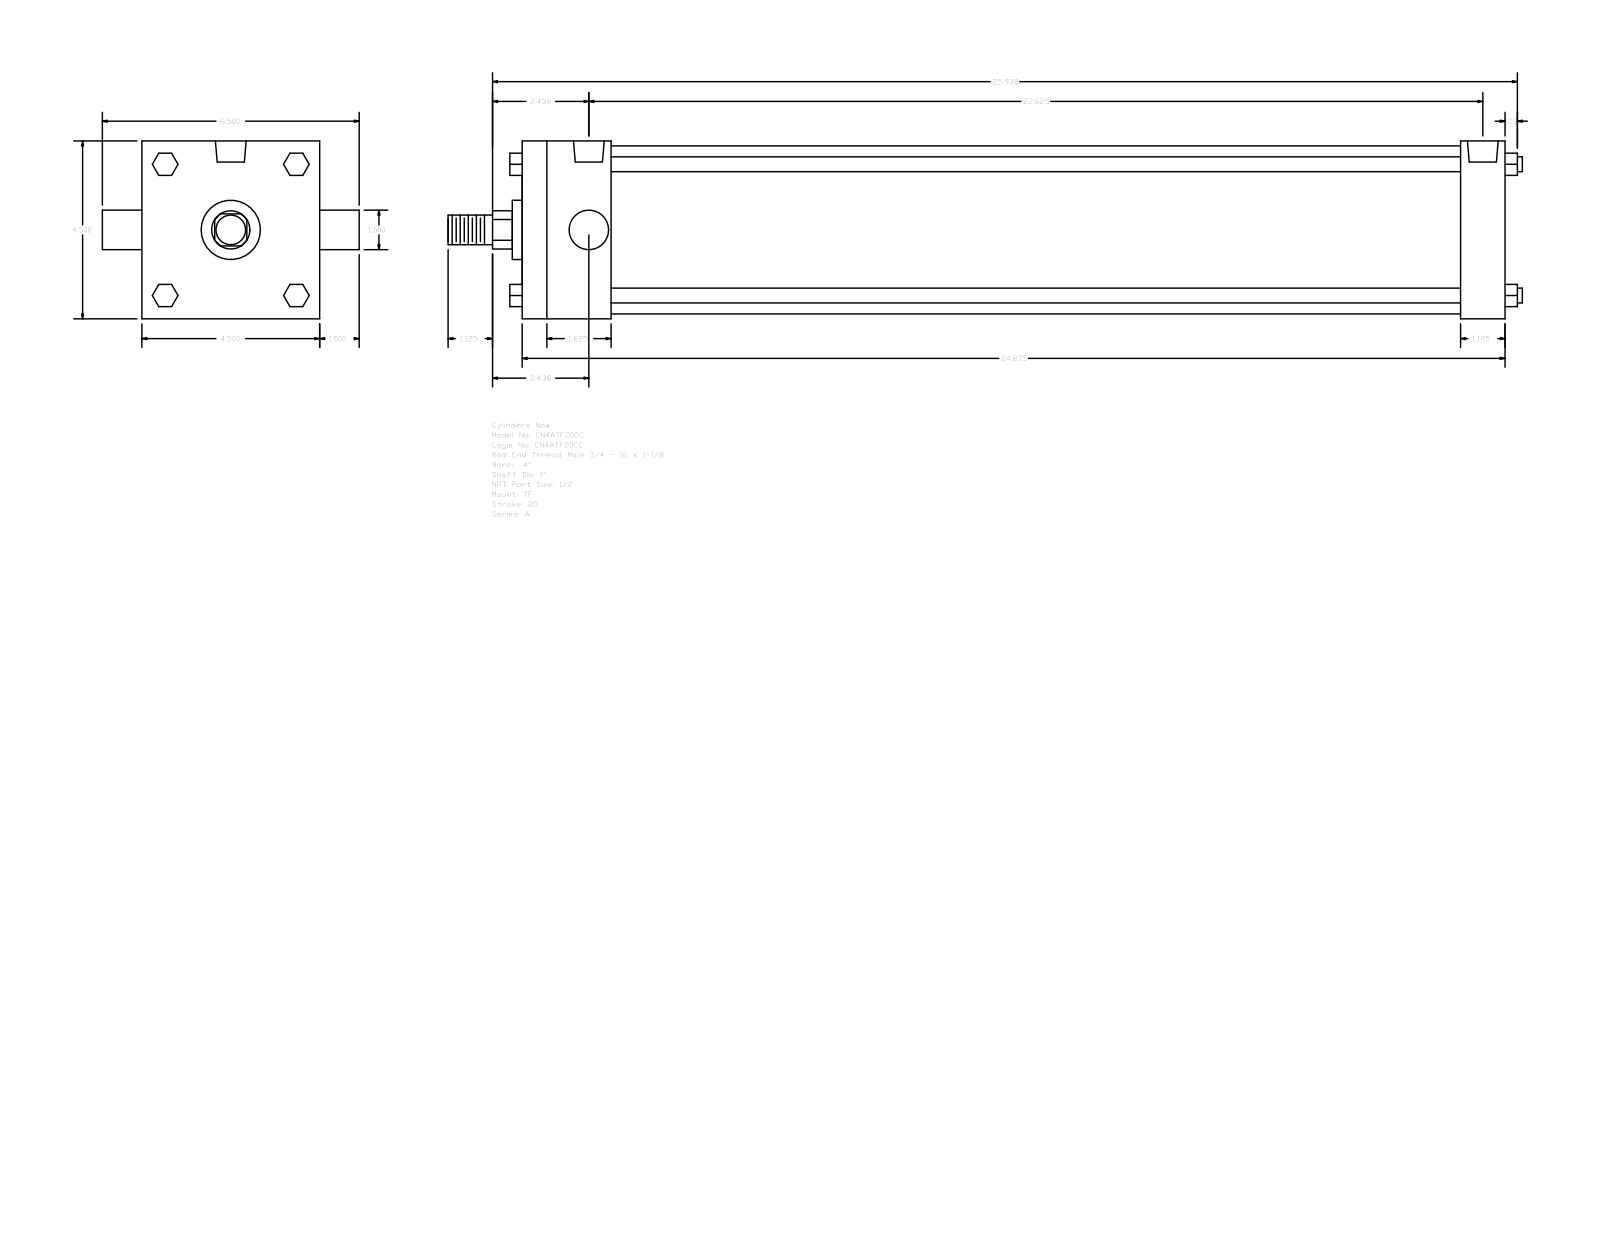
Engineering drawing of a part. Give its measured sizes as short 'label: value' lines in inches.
name: A_TF__0400_1
written by: GSSL Pune (CONFIG_CONTROL_DESIGN)
unit: in
bodies: 0 solids, 120 faces (92 planar, 28 cylindrical, 0 other)
size: 27.187 × 6.5 × 4.5
holes: 3× ⌀0.344, 2× ⌀0.778
bosses: 4× ⌀0.375, 2× ⌀1, 1× ⌀4.25, 1× ⌀1.5, 1× ⌀0.75
rounds: 1× R0.484
face distances: 4.5, 24.875, 23.75, 1.125, 2.25, 21.5, 22.625, 0.563, 1.66, 2.875
hole spacings: 0.125, 22.5, 22.375, 22.625
